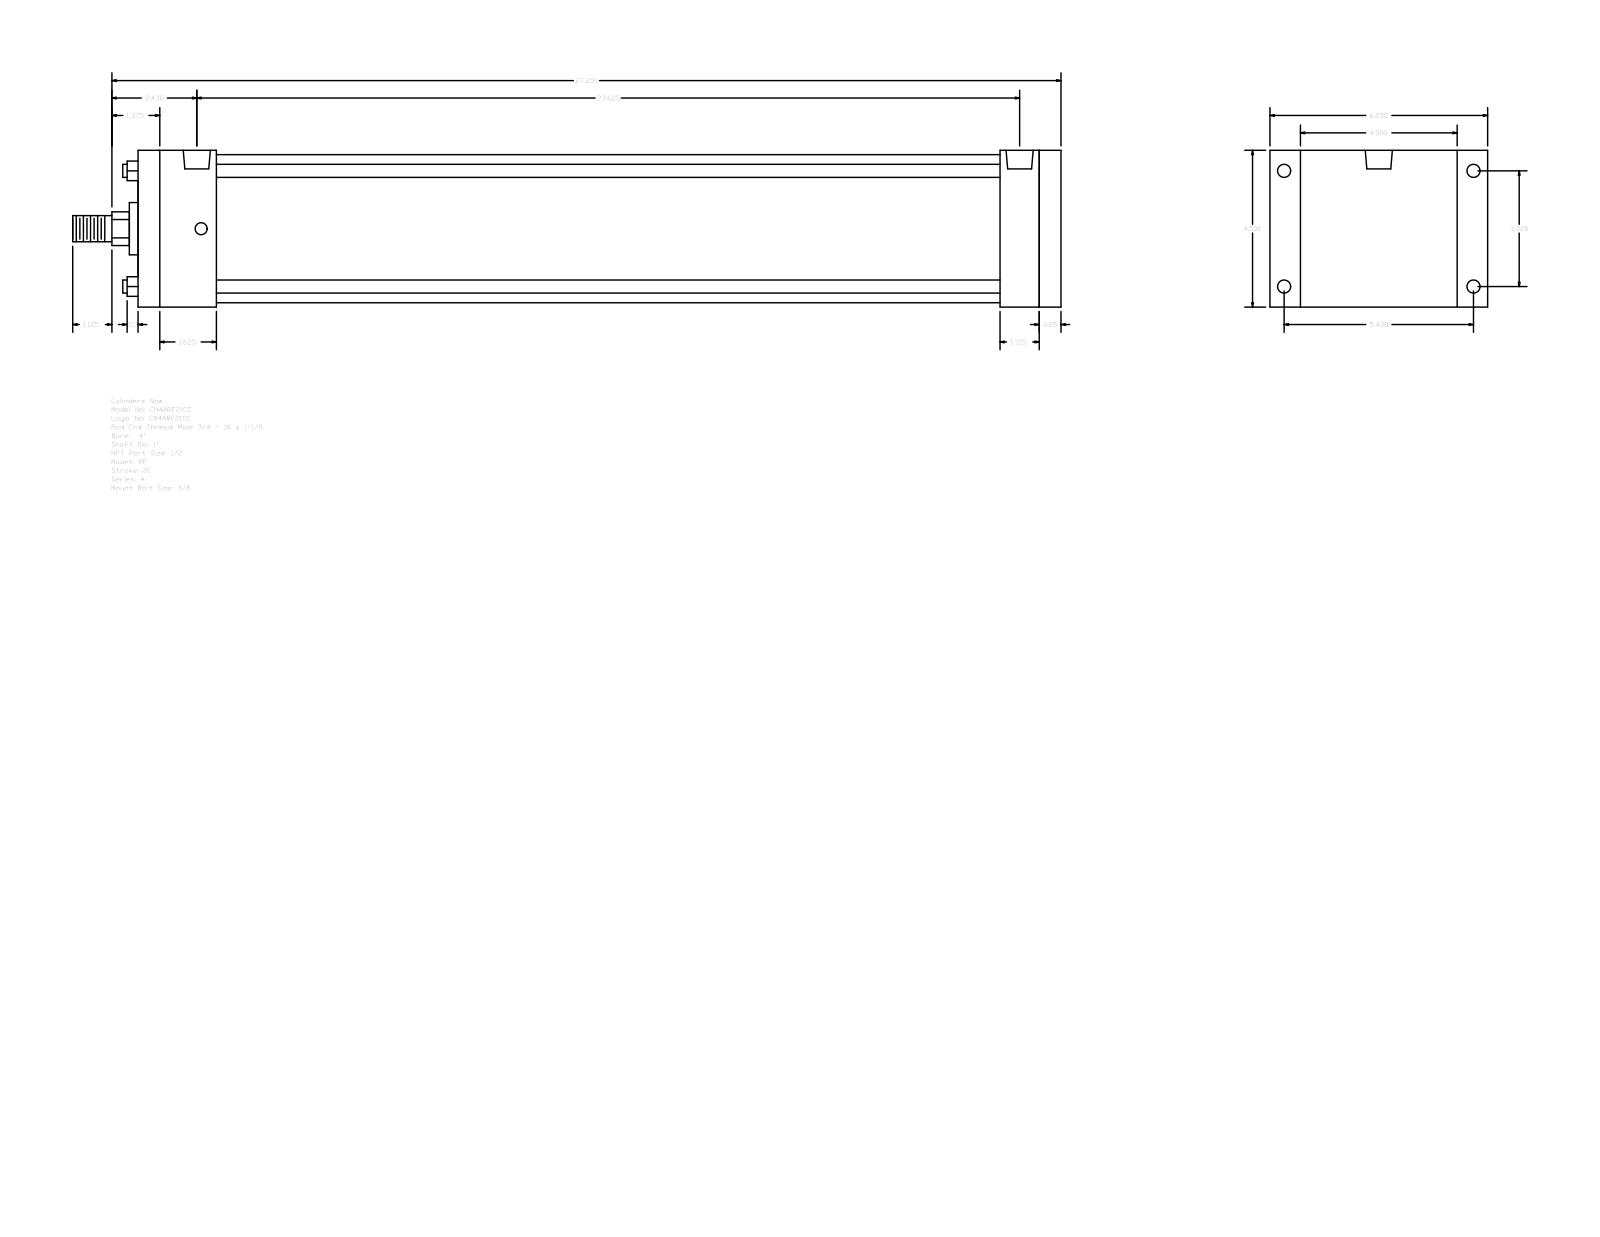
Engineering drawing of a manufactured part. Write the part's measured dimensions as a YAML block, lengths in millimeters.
part_name: "A_RF__0400_1"
step_written_by: "GSSL Pune (CONFIG_CONTROL_DESIGN)"
units: millimeters
bodies: {solids: 0, faces: 92, planar: 64, cylindrical: 28, other: 0}
overall_size: [720.73, 158.75, 114.3]
round_holes:
  - {diameter: 8.73, count: 4}
  - {diameter: 9.53, count: 4}
  - {diameter: 19.77, count: 2}
round_bosses_or_shafts:
  - {diameter: 9.53, count: 4}
  - {diameter: 107.95, count: 1}
  - {diameter: 38.1, count: 1}
  - {diameter: 25.4, count: 1}
  - {diameter: 19.05, count: 1}
partial_cylinders:
  - {radius: 12.29, count: 1}
face_to_face_distances: [114.3, 673.1, 657.22, 15.88, 28.57, 22.23, 136.53, 628.65, 44.45, 57.15]
hole_center_spacings: [3.18, 84.32, 138.12, 161.82, 593.72, 596.9, 600.08]
